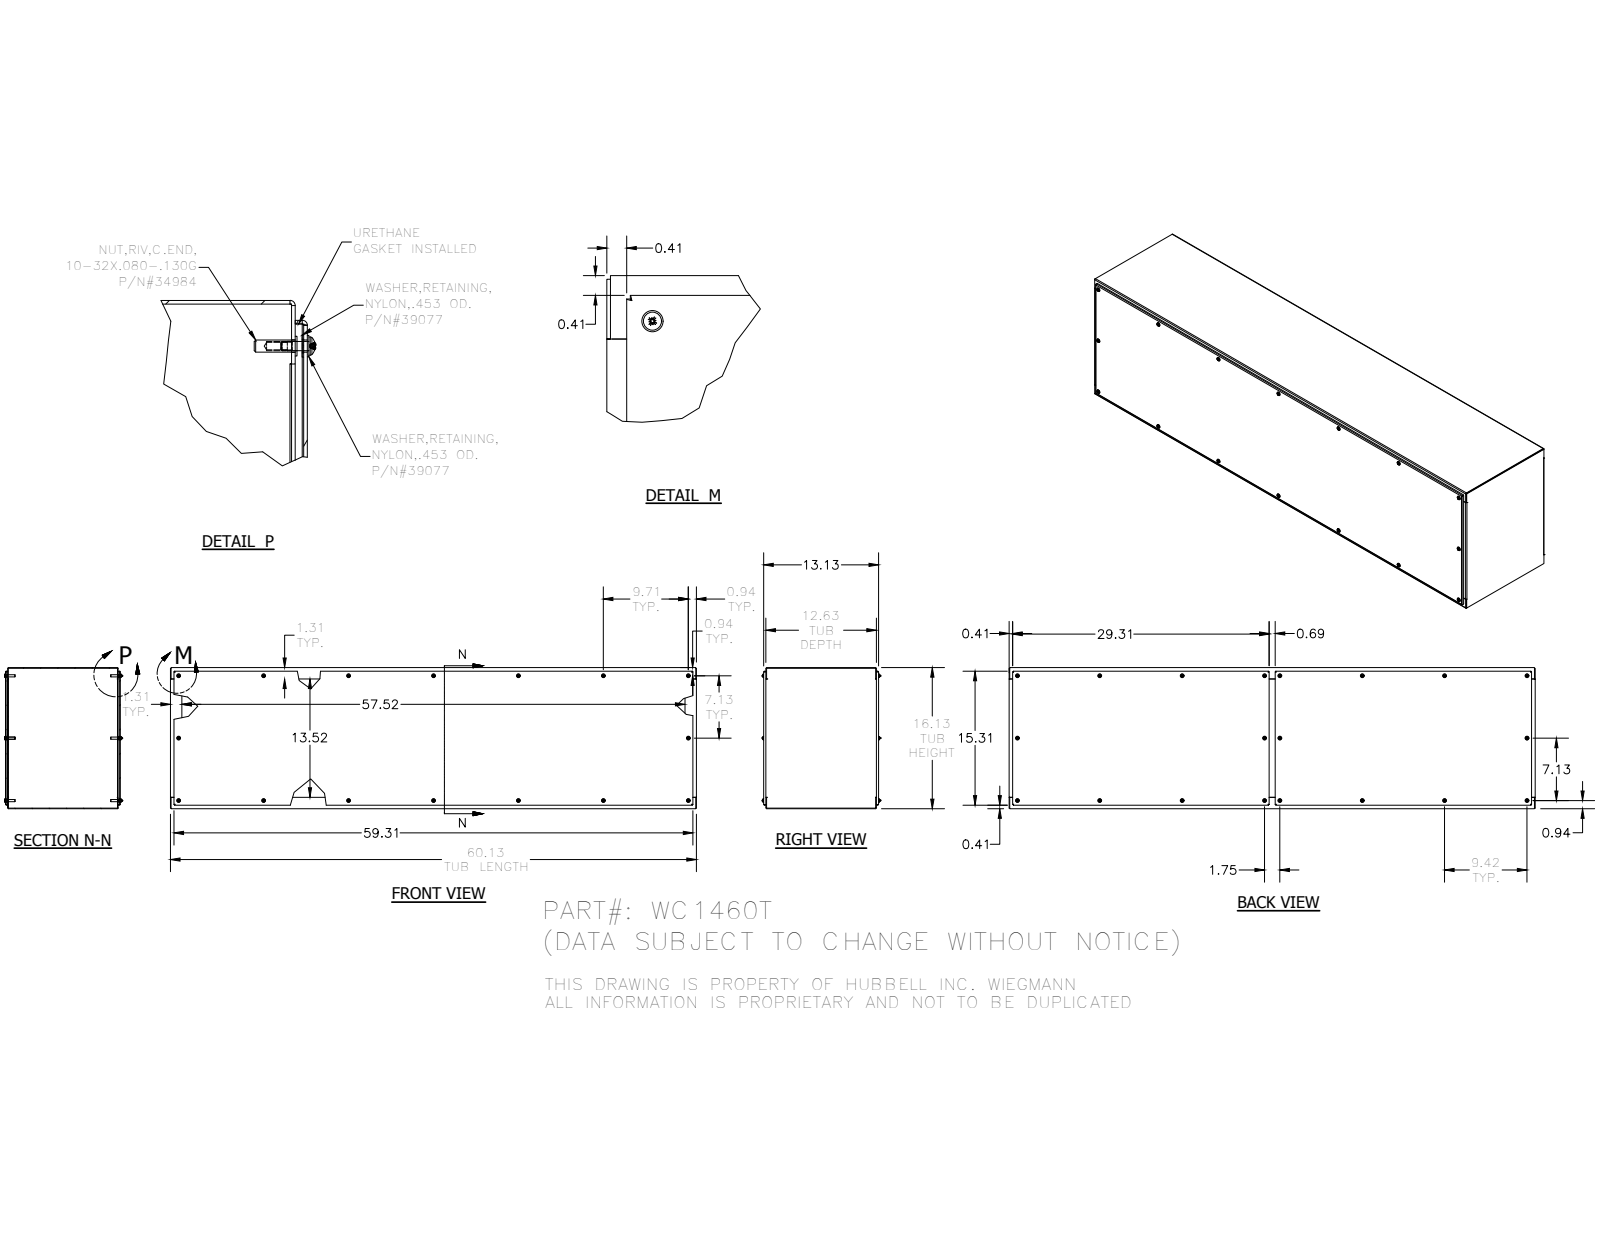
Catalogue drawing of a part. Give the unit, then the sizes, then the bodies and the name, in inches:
Units: inches
Overall size (bounding box): 60.125 × 16.125 × 13.451
Round holes (diameter × count): ⌀0.278 ×34, ⌀0.25 ×33, ⌀0.156 ×32, ⌀0.188 ×32, ⌀0.196 ×32, ⌀0.257 ×28
Round bosses / shafts (diameter × count): ⌀0.453 ×34, ⌀0.373 ×34, ⌀0.19 ×34, ⌀0.437 ×32, ⌀0.406 ×32, ⌀0.248 ×32
Partial cylindrical surfaces — rounded edges, fillets, slot ends (radius × count): R0.089 ×34, R0.031 ×18, R0.105 ×18
Main face-to-face distances: 0.074, 13.051, 16.051, 12.977, 13.125, 0.25, 12.801, 15.977, 16.125, 12.875
Hole centre spacings: 9.708, 14.25, 17.243, 17.081, 30, 9.417, 24.085, 33.213
Volume: 309.8 in³ · Surface area: 8 469 in²
Bodies: 158 solids, 3070 faces (1590 planar, 638 cylindrical, 842 other)
Part name (STEP PRODUCT): 34984; WC14TLRS; WC1460TTB; 39035 (+6 more)
STEP written by: Autodesk Inventor 2016 (AUTOMOTIVE_DESIGN)
